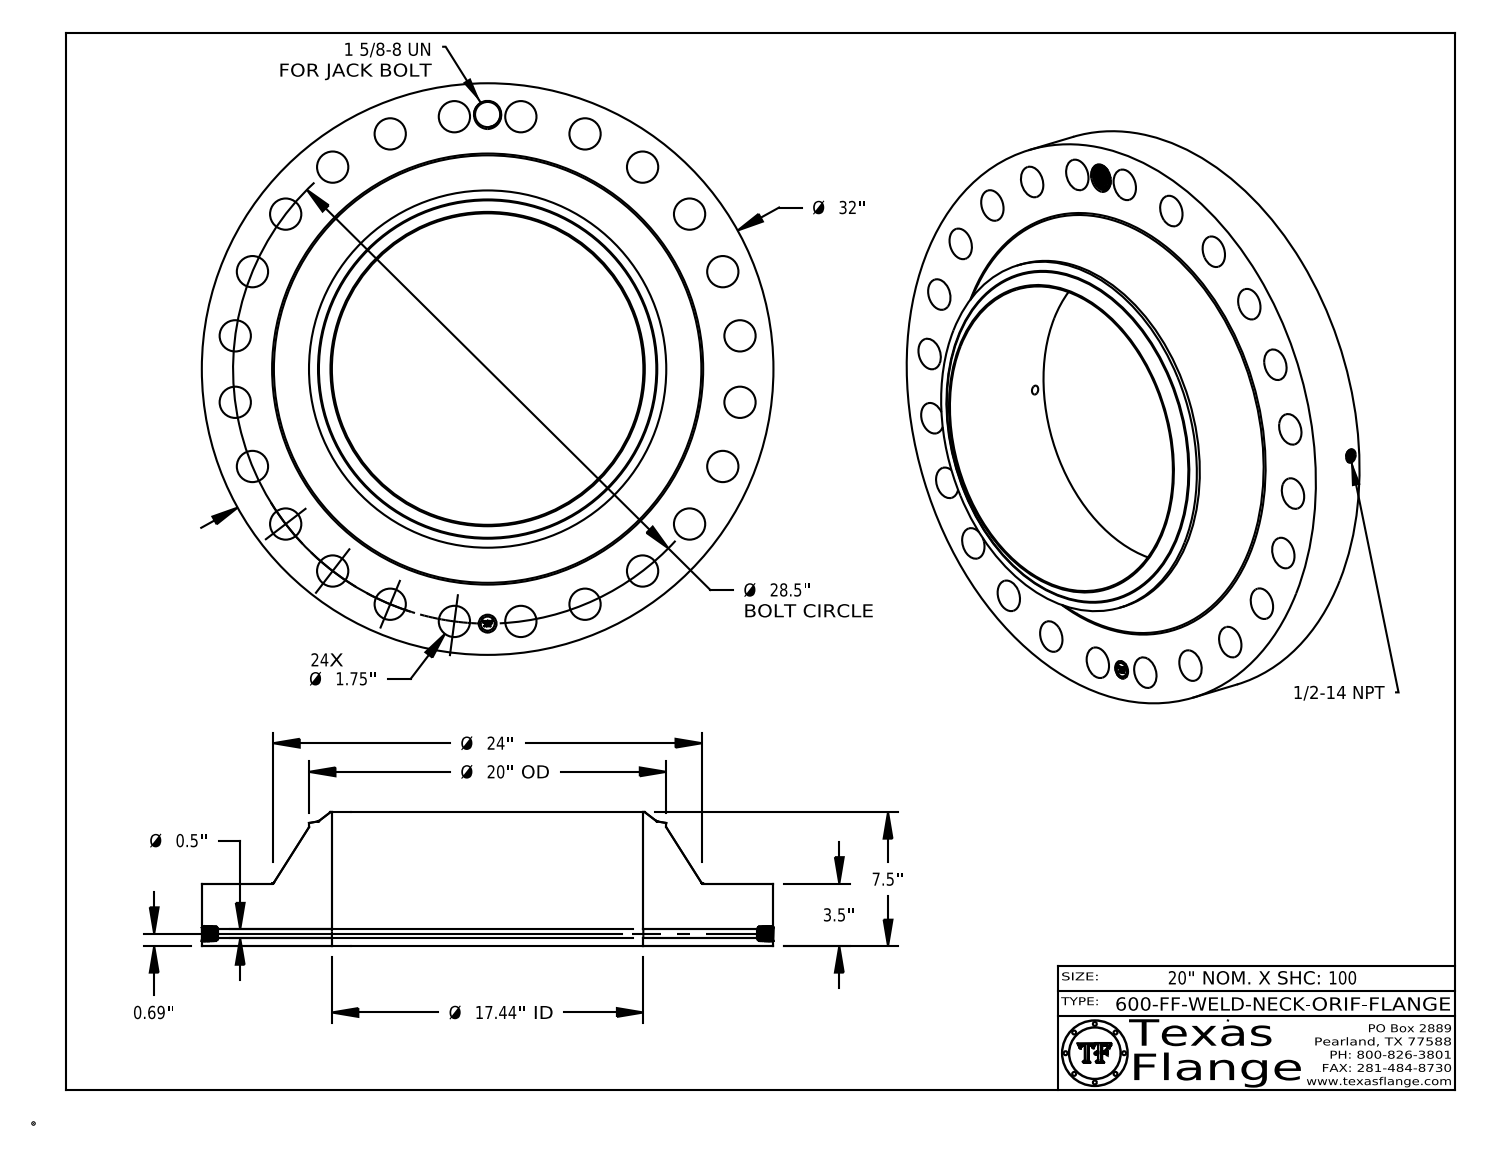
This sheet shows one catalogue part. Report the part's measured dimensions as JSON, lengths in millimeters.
{"part_name": "600-FF-WELD-NECK", "step_written_by": "CATIA V5 STEP AP214 (AUTOMOTIVE_DESIGN)", "units": "millimeters", "bodies": {"solids": 1, "faces": 880, "planar": 368, "cylindrical": 149, "other": 363}, "overall_size": [812.8, 812.8, 190.5], "volume_mm3": 36900000, "surface_area_mm2": 1574000, "round_holes": [[44.5, 24], [12.7, 1], [17.1, 1], [25.4, 1], [35.8, 1], [442.9, 1]], "round_bosses_or_shafts": [[1.5, 8], [812.8, 1], [508, 1], [20, 1]], "face_to_face_distances": [88.9, 190.5, 101.6, 88.5, 0.4, 102, 7.6, 7.4, 1.4, 6.3], "hole_center_spacings": [362, 440.7, 626.9, 717.7, 277, 94.5, 187.4, 511.9]}
